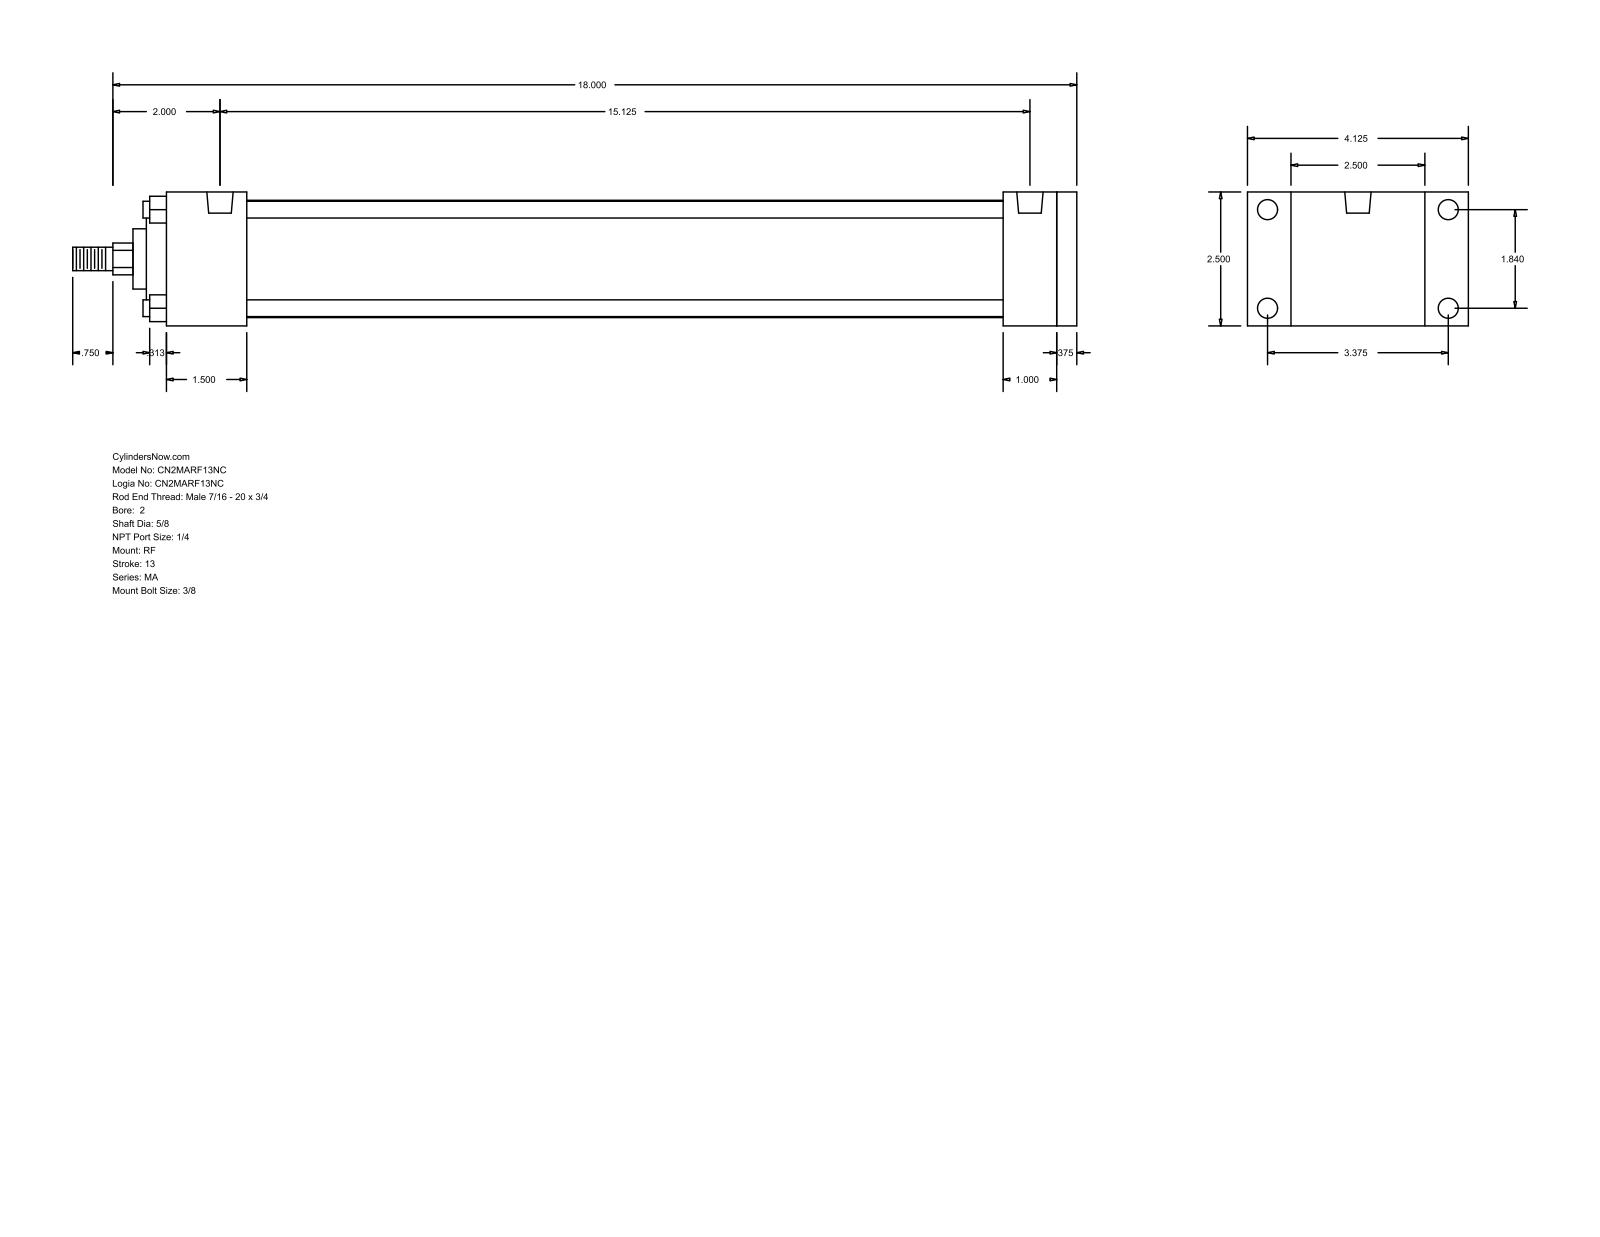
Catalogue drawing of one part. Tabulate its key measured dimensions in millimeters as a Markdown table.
| quantity | value |
| --- | --- |
| part name | MA_RF__0200_0.625 |
| STEP written by | GSSL Pune (CONFIG_CONTROL_DESIGN) |
| units | millimeters |
| bodies | 0 solids, 94 faces (65 planar, 29 cylindrical, 0 other) |
| overall size | 476.25 × 104.78 × 63.5 |
| round holes (diameter × count) | 7.94 × 4, 9.53 × 4, 12.49 × 2 |
| round bosses / shafts (diameter × count) | 7.94 × 4, 55.63 × 1, 50.8 × 1, 28.57 × 1, 15.88 × 1, 11.11 × 1 |
| partial cylindrical surfaces (radius × count) | 7.54 × 1 |
| main face-to-face distances | 63.5, 9.52, 431.8, 38.1, 34.93, 441.32, 422.28, 384.18, 393.7, 396.87 |
| hole center spacings | 46.74, 85.72, 97.63, 384.18 |
